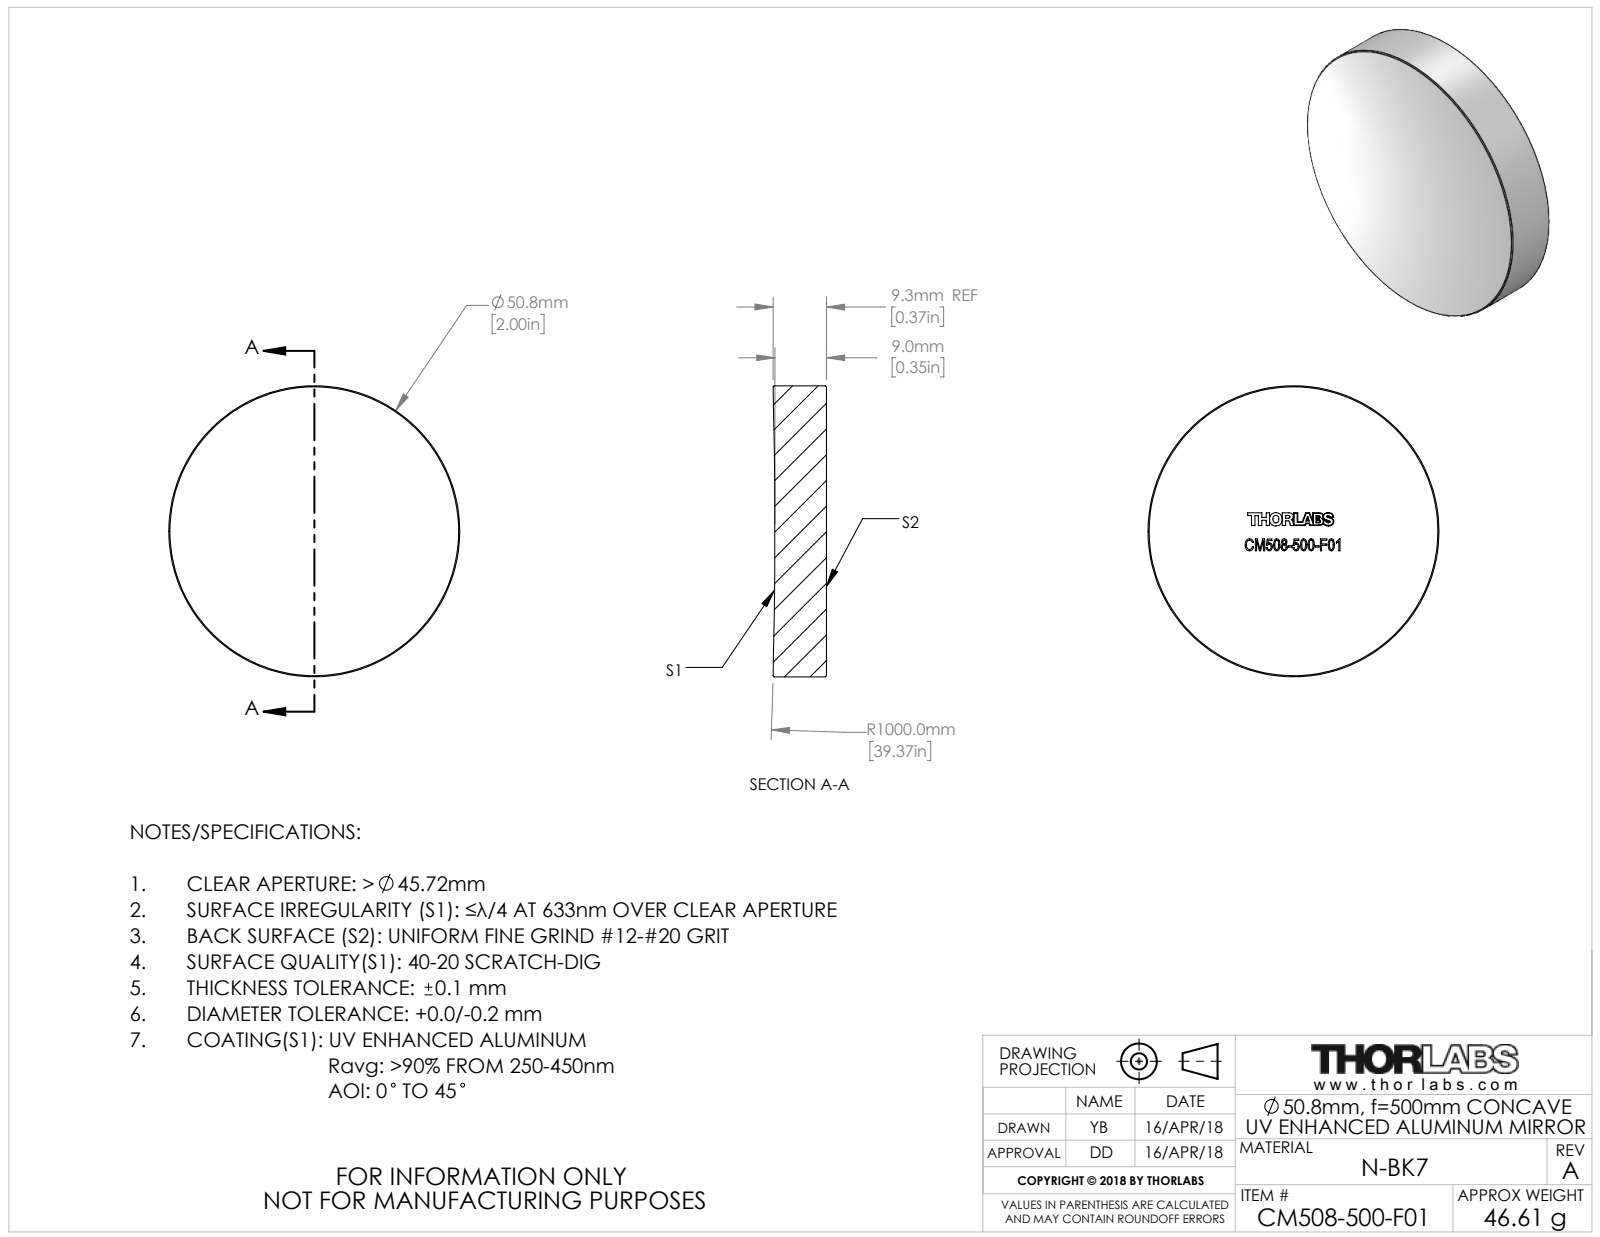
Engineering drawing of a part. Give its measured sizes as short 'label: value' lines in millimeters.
name: TTN153321-E0W
written by: SolidWorks 2018 (CONFIG_CONTROL_DESIGN)
unit: mm
bodies: 1 solid, 43 faces (35 planar, 2 cylindrical, 6 other)
size: 50.8 × 50.8 × 9.32
volume: 18 562 mm³; area: 5 504 mm²
bosses: 1× ⌀50.8
